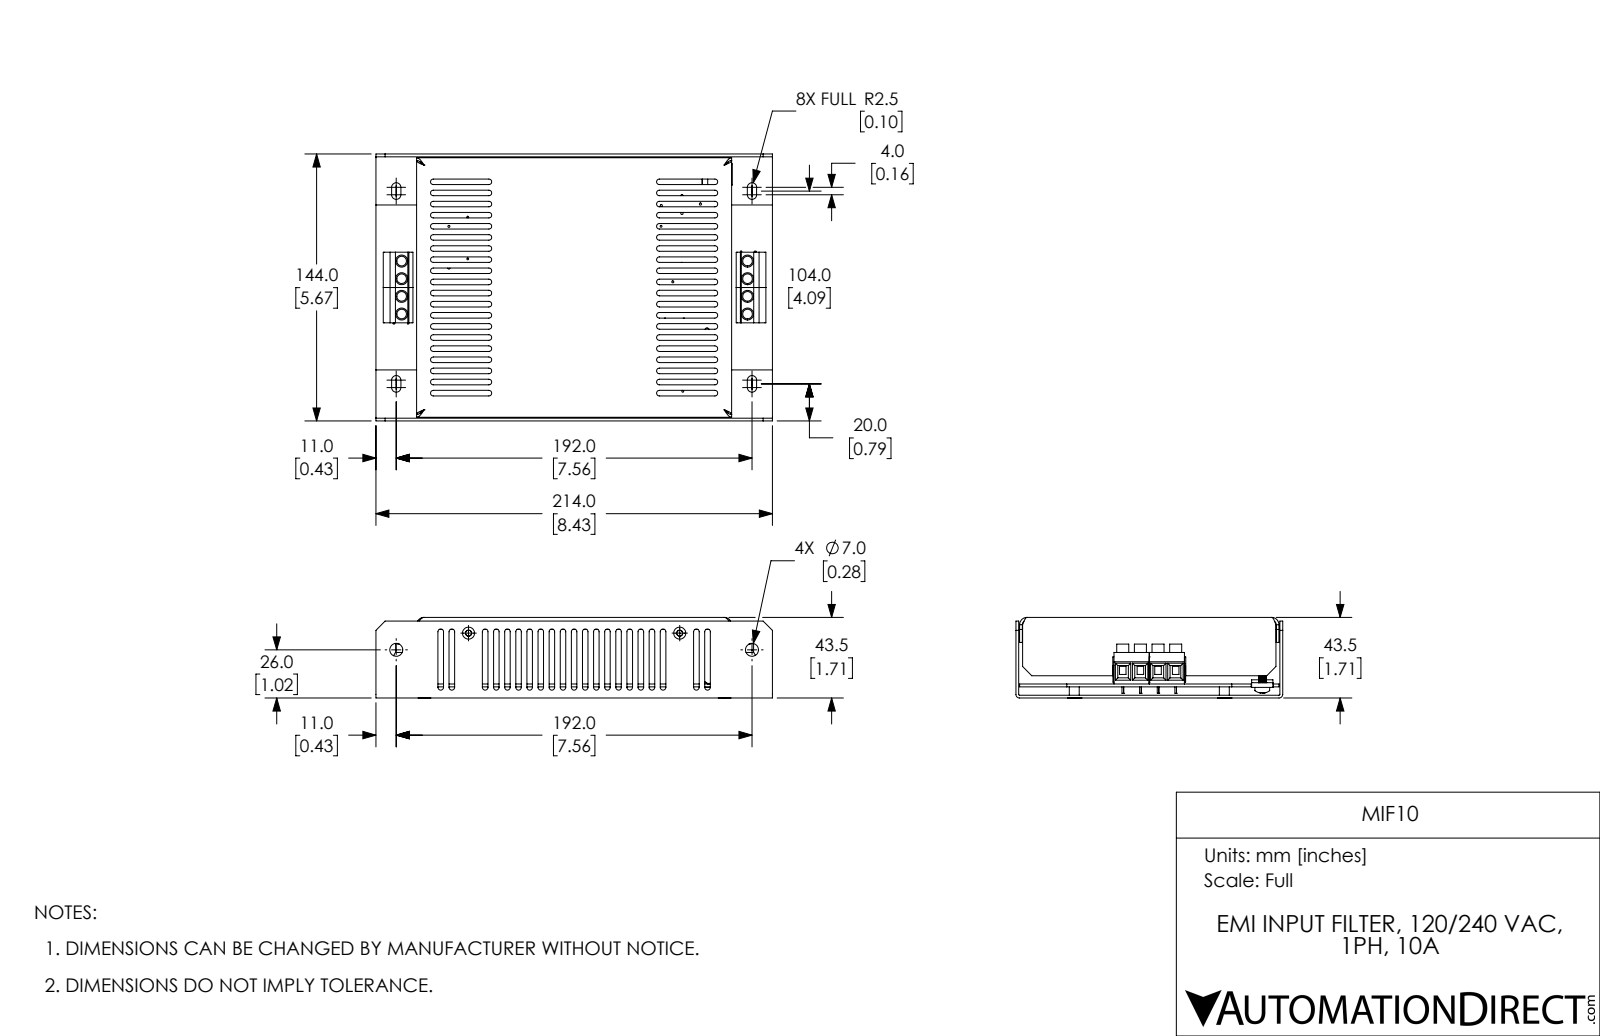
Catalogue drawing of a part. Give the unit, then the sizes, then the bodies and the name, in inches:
Units: inches
Overall size (bounding box): 8.425 × 5.669 × 1.713
Round holes (diameter × count): ⌀0.056 ×36, ⌀0.165 ×12, ⌀0.138 ×10, ⌀0.085 ×8, ⌀0.044 ×6, ⌀0.04 ×4, ⌀0.048 ×4, ⌀0.079 ×4, ⌀0.09 ×4, ⌀0.157 ×4, ⌀0.16 ×4, ⌀0.052 ×2
Round bosses / shafts (diameter × count): ⌀0.268 ×8, ⌀0.11 ×4, ⌀0.126 ×2
Partial cylindrical surfaces — rounded edges, fillets, slot ends (radius × count): R0.059 ×138, R0.024 ×12, R0.02 ×10, R0.098 ×8, R0.343 ×8, R0.509 ×8, R0.079 ×6, R0.039 ×4
Main face-to-face distances: 0.059, 1.654, 0.24, 0.177, 0.299, 0.236, 0.063, 0.067, 0.17, 0.233
Hole centre spacings: 0.858, 1, 1.083, 3.2, 0.2, 0.559, 0.8, 0.881
Volume: 10.89 in³ · Surface area: 438.9 in²
Bodies: 19 solids, 1771 faces (1100 planar, 577 cylindrical, 94 other)
Part name (STEP PRODUCT): MIF10-16
STEP written by: SolidWorks 2017 (AUTOMOTIVE_DESIGN)
